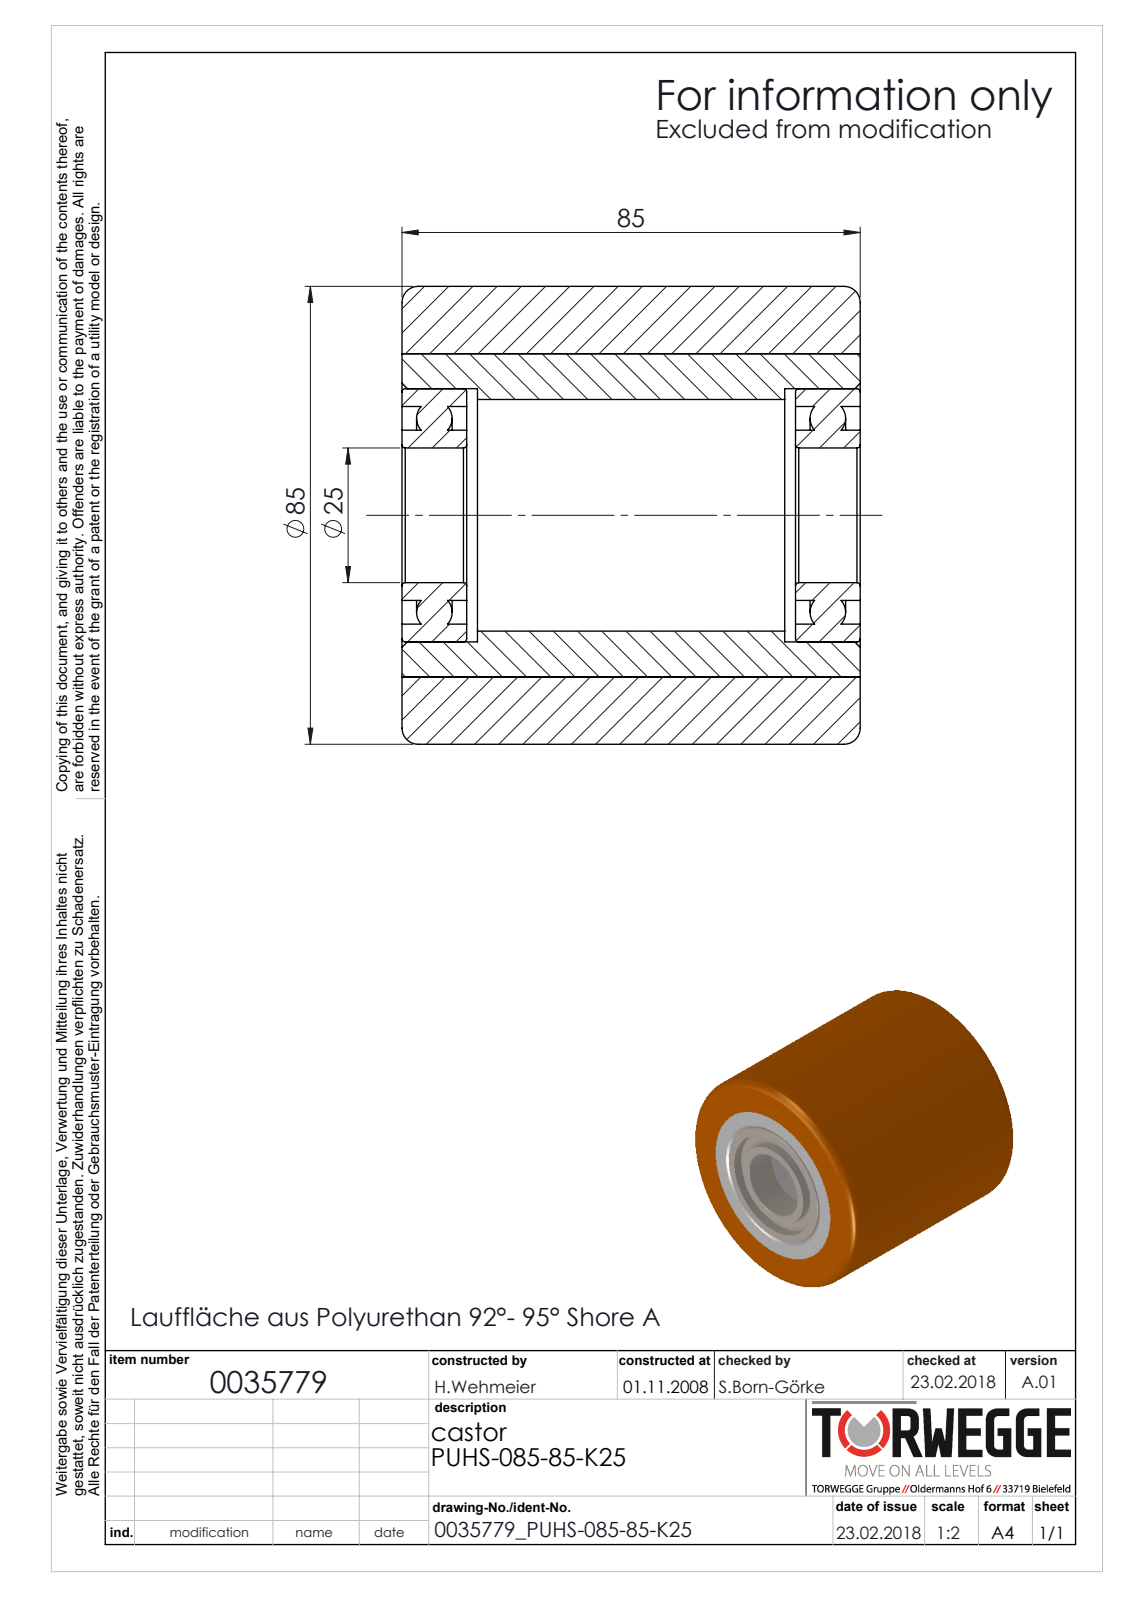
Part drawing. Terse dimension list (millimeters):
name: 0035779_PUHS-085-85-K25
written by: SolidWorks 2018 (AUTOMOTIVE_DESIGN)
unit: mm
bodies: 4 solids, 48 faces (14 planar, 18 cylindrical, 16 other)
size: 85 × 85 × 85
volume: 373 701 mm³; area: 87 719 mm²
holes: 1× ⌀25, 1× ⌀40.4, 1× ⌀43, 1× ⌀47, 1× ⌀60
bosses: 1× ⌀85, 1× ⌀31.6
face distances: 85, 12, 73, 61, 14, 71, 2, 59, 57
